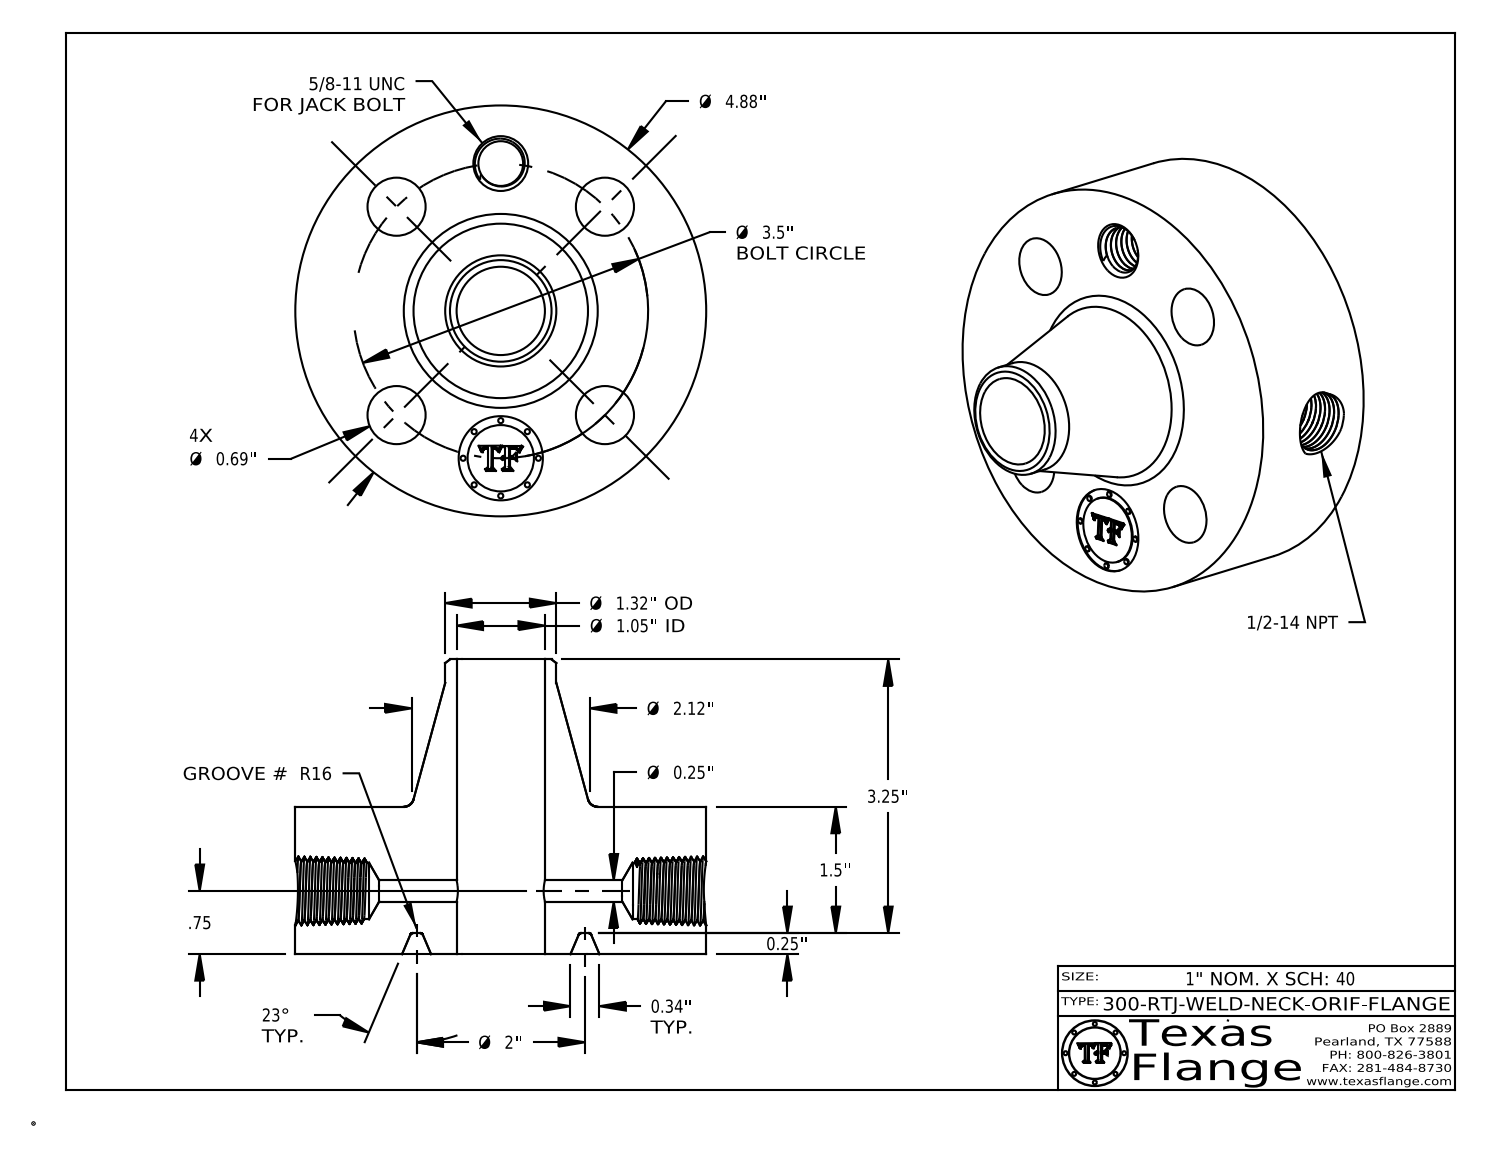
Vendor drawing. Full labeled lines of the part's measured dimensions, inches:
Part name (STEP PRODUCT): 300-RTJ-WELD-NECK
STEP written by: CATIA V5 STEP AP214 (AUTOMOTIVE_DESIGN)
Units: inches
Bodies: 1 solid, 789 faces (370 planar, 91 cylindrical, 328 other)
Overall size (bounding box): 4.88 × 4.88 × 3.5
Volume: 29.25 in³ · Surface area: 107.6 in²
Round holes (diameter × count): ⌀0.69 ×4, ⌀0.25 ×1, ⌀0.531 ×1, ⌀0.672 ×1, ⌀1 ×1, ⌀1.049 ×1
Round bosses / shafts (diameter × count): ⌀0.061 ×8, ⌀4.88 ×1, ⌀1.32 ×1, ⌀0.788 ×1
Main face-to-face distances: 1.75, 0.25, 1.5, 1.735, 1.485, 0.015, 3.5, 3.25, 1.765, 0.298
Hole centre spacings: 1.75, 1.339, 2.475, 3.233, 3.5
